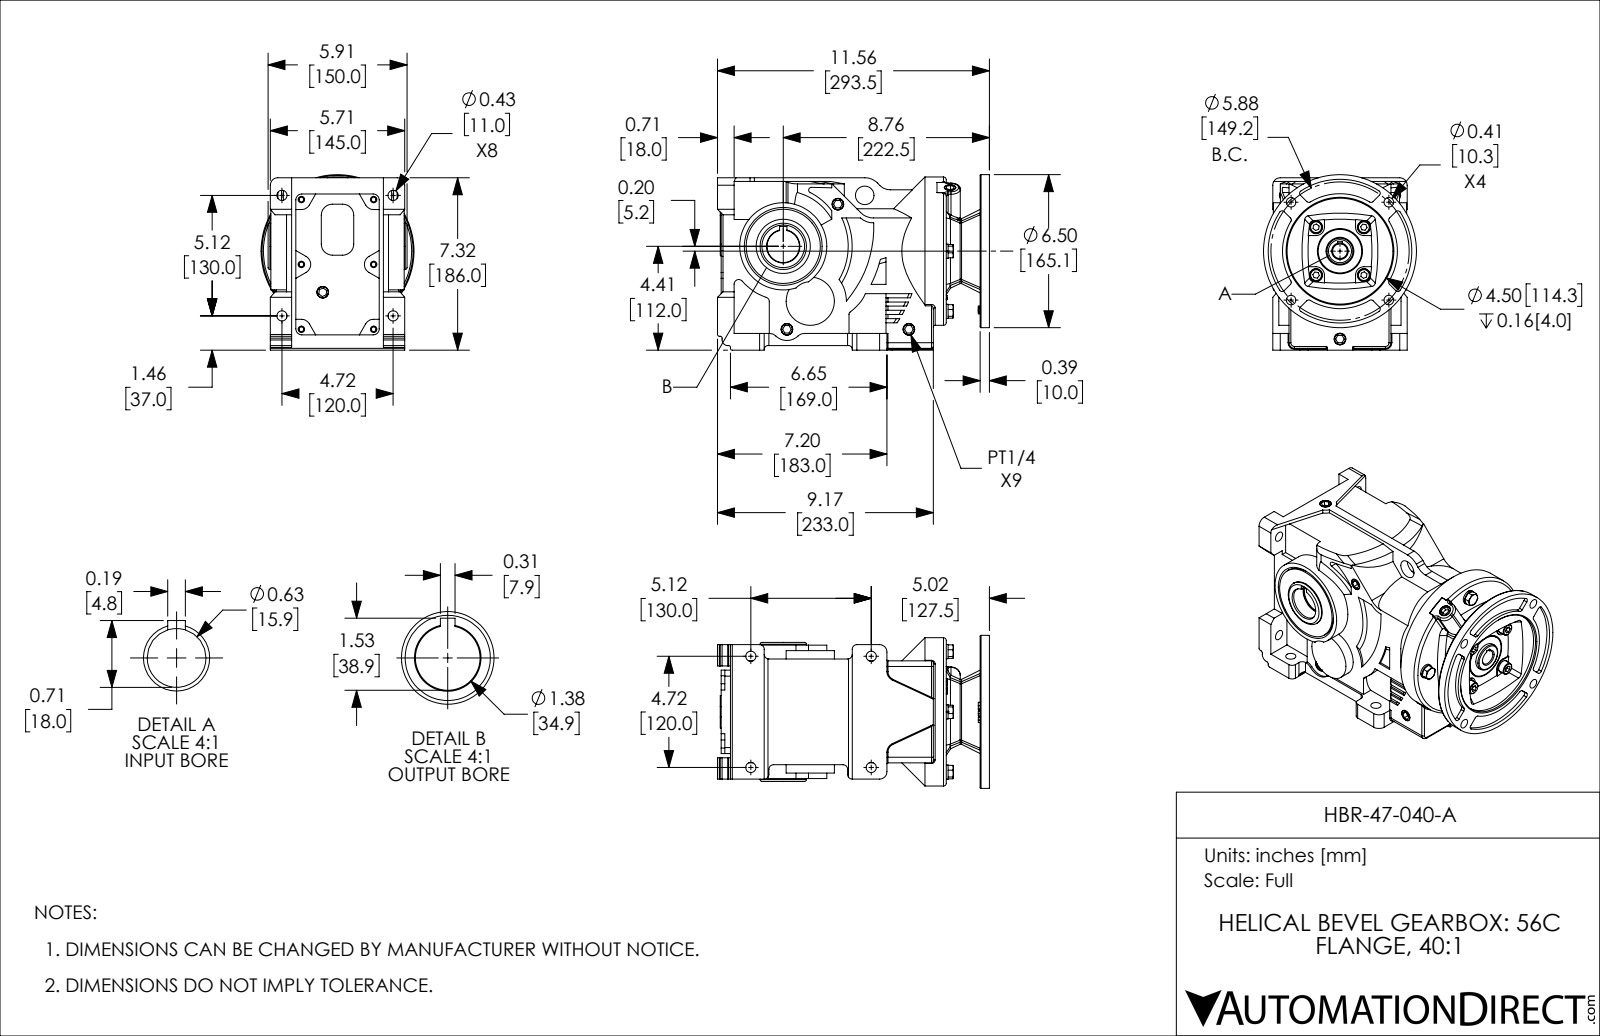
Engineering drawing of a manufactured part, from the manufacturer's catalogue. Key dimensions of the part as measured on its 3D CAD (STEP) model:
Part name (STEP PRODUCT): HBR-47-040-A
STEP written by: SolidWorks 2018 (AUTOMOTIVE_DESIGN)
Units: inches
Bodies: 1 solid, 1002 faces (447 planar, 317 cylindrical, 238 other)
Overall size (bounding box): 11.555 × 7.455 × 6.5
Volume: 308.7 in³ · Surface area: 495.3 in²
Round holes (diameter × count): ⌀0.433 ×8, ⌀0.197 ×6, ⌀0.276 ×6, ⌀0.323 ×4, ⌀0.354 ×4, ⌀0.406 ×4, ⌀0.551 ×4, ⌀0.625 ×1, ⌀0.787 ×1, ⌀0.846 ×1, ⌀1.375 ×1, ⌀1.457 ×1
Round bosses / shafts (diameter × count): ⌀0.606 ×4, ⌀0.512 ×4, ⌀0.315 ×4, ⌀6.5 ×1, ⌀6.299 ×1, ⌀3.701 ×1, ⌀3.15 ×1, ⌀2.047 ×1
Partial cylindrical surfaces — rounded edges, fillets, slot ends (radius × count): R0.118 ×22, R0.079 ×18, R0.394 ×12, R0.197 ×10, R0.472 ×9, R0.039 ×5, R0.256 ×4, R0.315 ×4
Main face-to-face distances: 0.197, 0.394, 0.236, 0.157, 11.004, 4.331, 0.118, 0.079, 11.24, 10.846
Hole centre spacings: 1.848, 2.132, 3.27, 3.717, 5.08, 5.118, 1.437, 1.5
